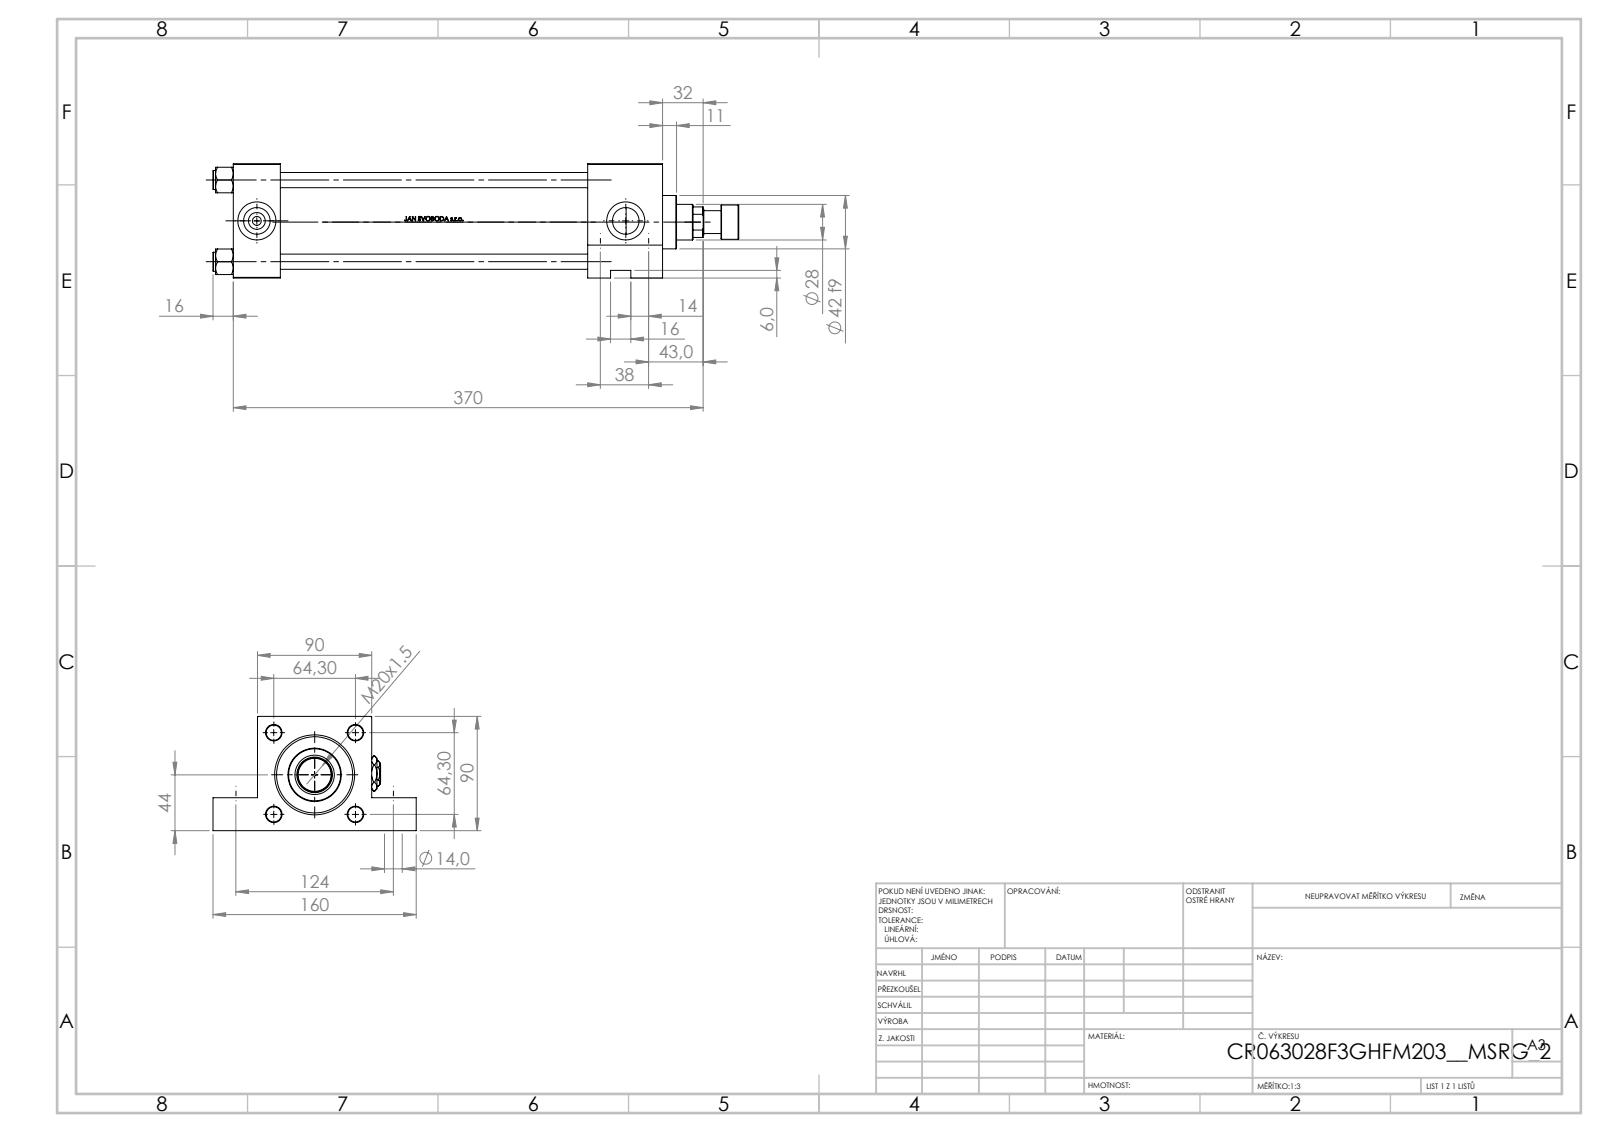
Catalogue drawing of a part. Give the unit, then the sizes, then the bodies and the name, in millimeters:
Units: millimetres
Overall size (bounding box): 414 × 160 × 90
Round holes (diameter × count): ⌀12 ×4, ⌀14 ×4, ⌀20.96 ×3, ⌀30 ×3, ⌀7 ×2, ⌀18.5 ×1, ⌀20 ×1, ⌀28 ×1, ⌀31 ×1, ⌀50 ×1, ⌀60 ×1, ⌀63 ×1
Round bosses / shafts (diameter × count): ⌀15 ×4, ⌀69 ×1, ⌀42 ×1, ⌀27 ×1, ⌀18 ×1
Main face-to-face distances: 90, 37, 301, 338, 279, 242, 59, 26, 64, 35
Hole centre spacings: 64.3, 38, 44.77, 46.18, 90.93, 124, 129.69, 10
Volume: 1 344 000 mm³ · Surface area: 321 496 mm²
Bodies: 14 solids, 1214 faces (488 planar, 138 cylindrical, 588 other)
Part name (STEP PRODUCT): V215_VC_A; NUT_M5_F; V215CR_VCP_F; V215CR_F_Body (+3 more)
STEP written by: SolidWorks 2019 (CONFIG_CONTROL_DESIGN)
